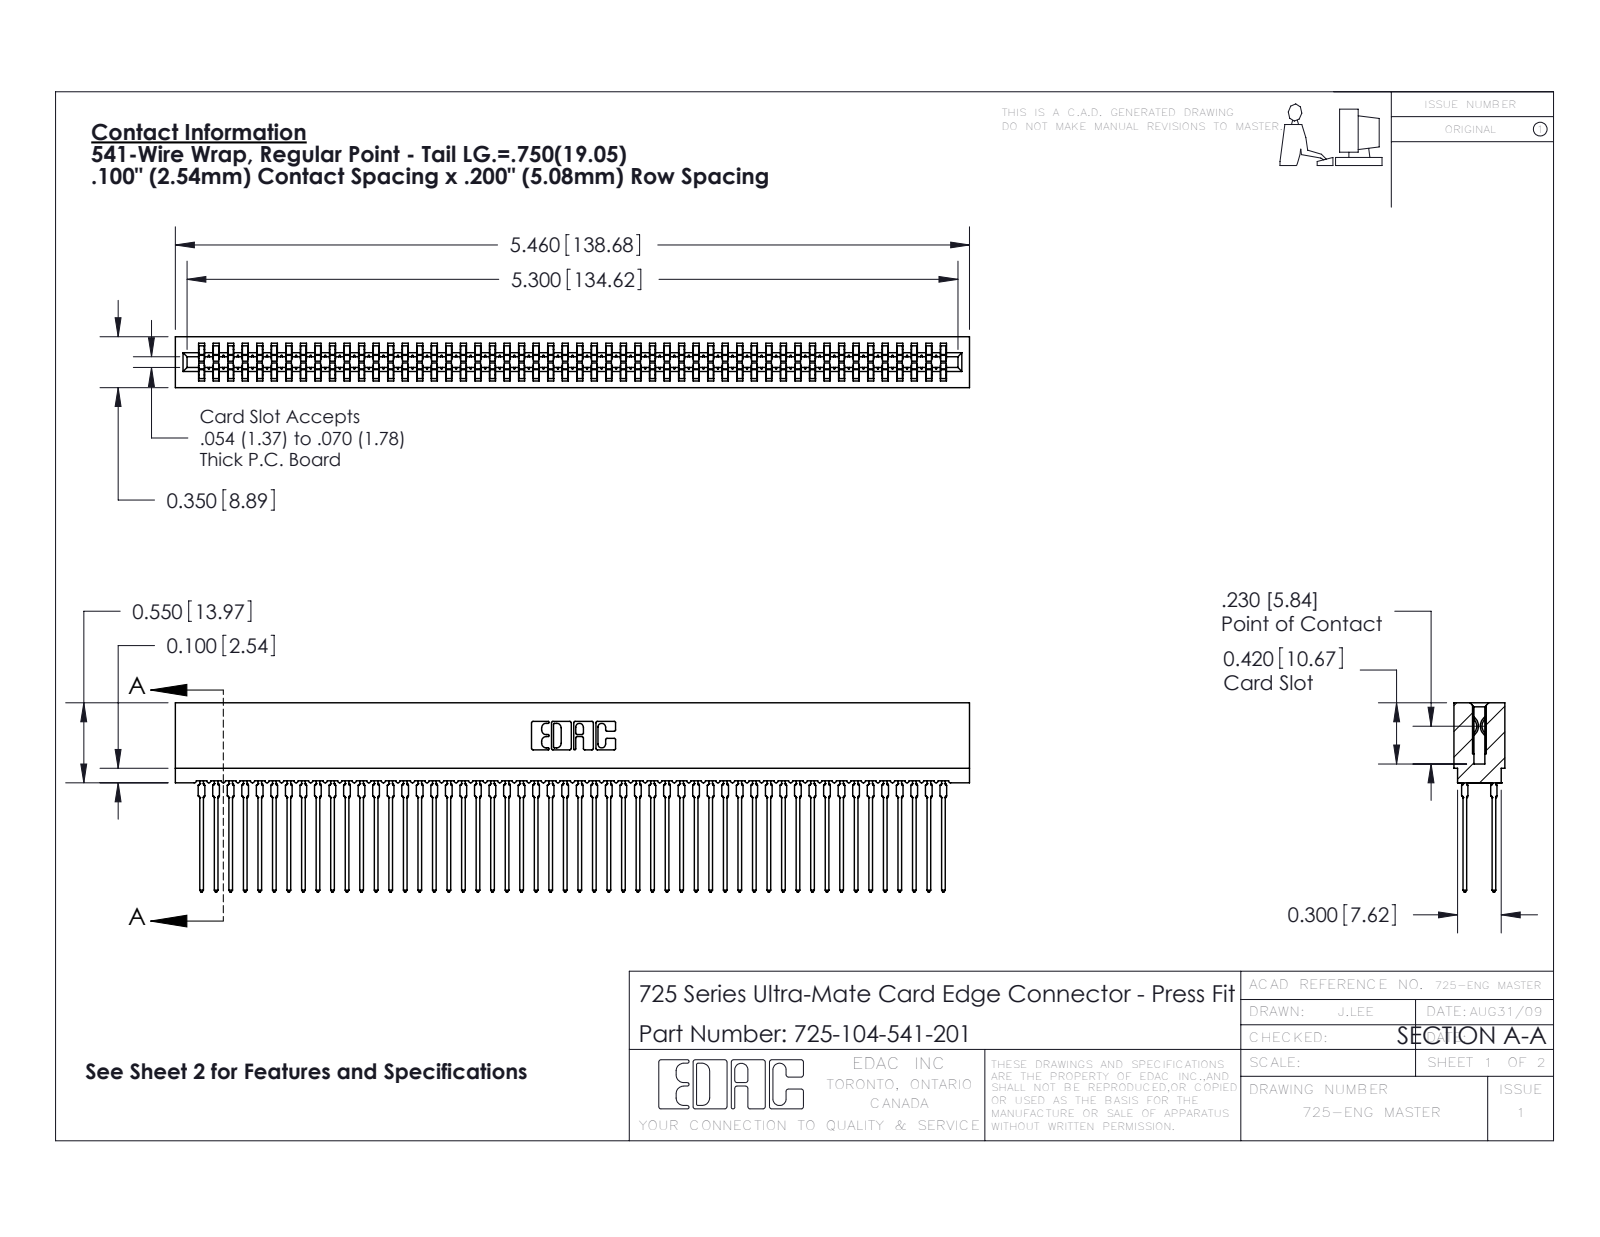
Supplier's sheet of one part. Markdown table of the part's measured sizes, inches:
| quantity | value |
| --- | --- |
| part name | 725-104-541-201; 745-292-001_541; 725 Part_Insulator Option - 01 |
| STEP written by | SolidWorks 2016 (CONFIG_CONTROL_DESIGN) |
| units | inches |
| bodies | 105 solids, 9403 faces (4839 planar, 1860 cylindrical, 2704 other) |
| overall size | 5.46 × 1.3 × 0.35 |
| volume | 0.699 in³ |
| surface area | 41.02 in² |
| partial cylindrical surfaces (radius × count) | 0.021 × 208, 0.015 × 104, 0.01 × 22, 0.005 × 8, 0.011 × 8, 0.007 × 6, 0.031 × 6, 0.026 × 3 |
| main face-to-face distances | 0.2, 0.063, 0.287, 0.087, 0.263, 0.025, 0.35, 0.212, 0.138, 0.076 |
